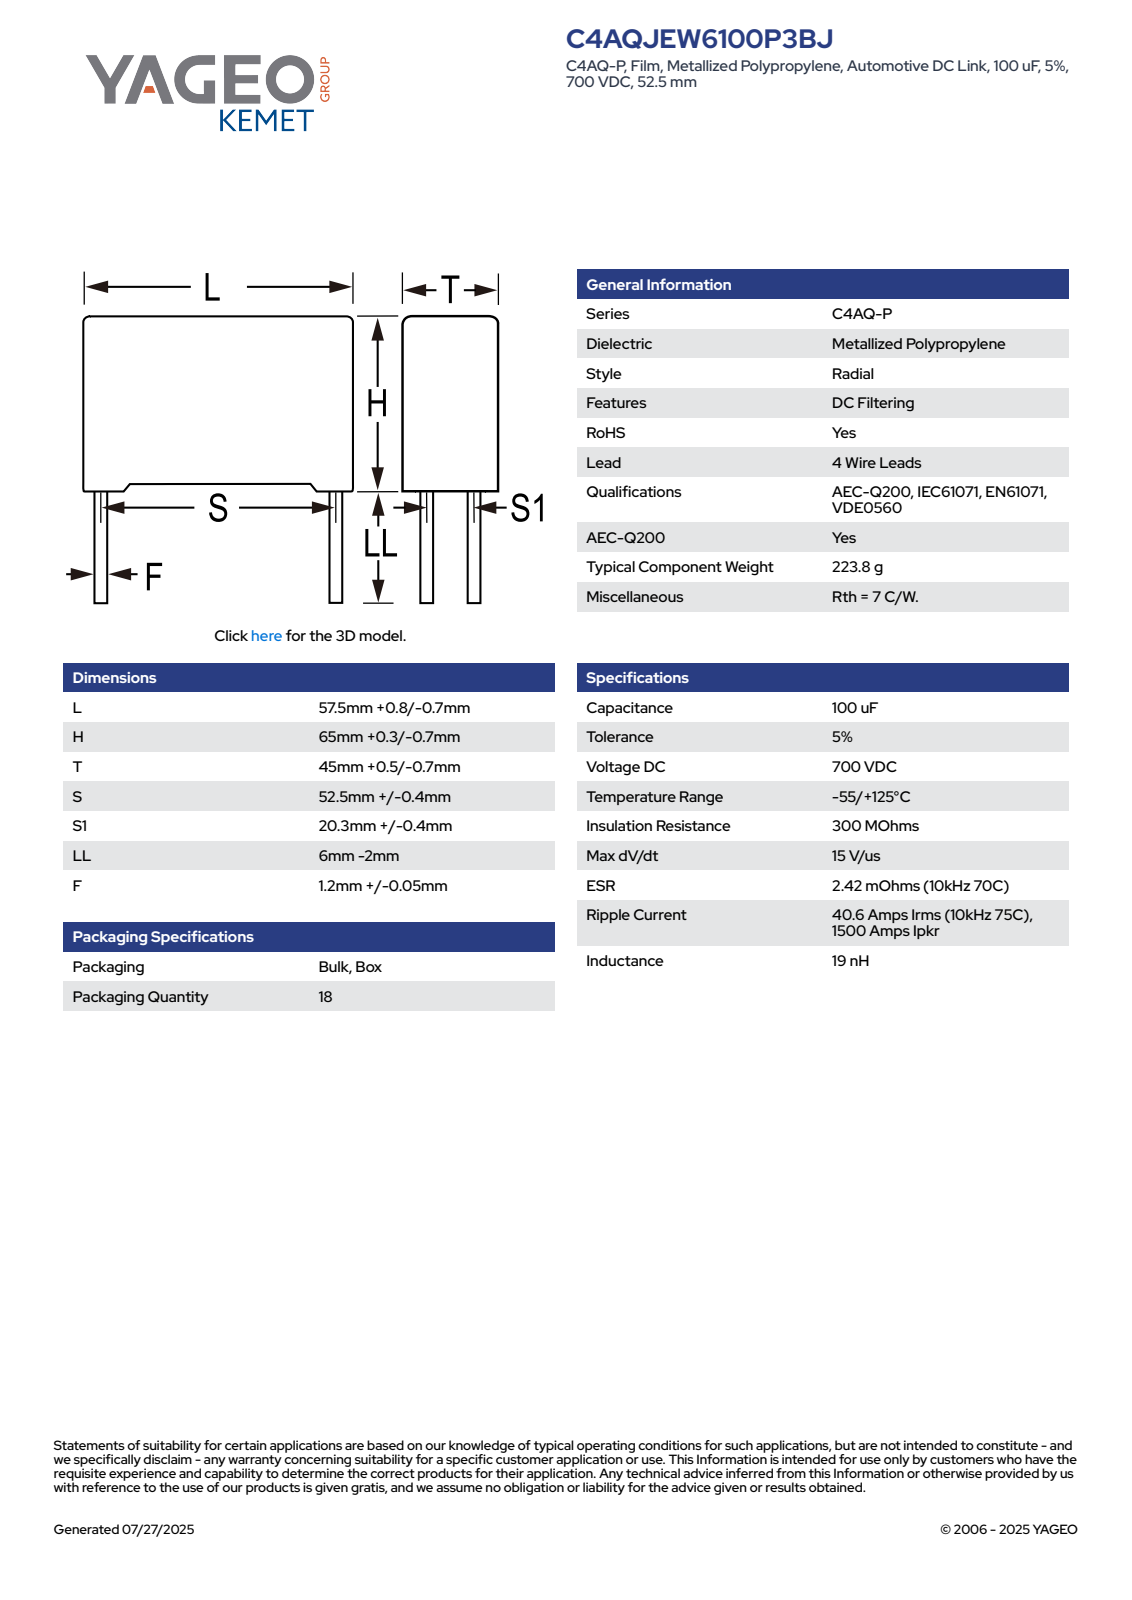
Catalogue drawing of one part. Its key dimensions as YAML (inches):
part_name: "CFP_RB4_57.5X65X45_L58.3H65.3T45.5S52.5S120.3LL4F1.25"
step_written_by: "SolidWorks 2014 (AUTOMOTIVE_DESIGN)"
units: inches
bodies: {solids: 4, faces: 91, planar: 83, cylindrical: 8, other: 0}
overall_size: [2.728, 2.295, 1.792]
volume: 10.3
surface_area: 29.75
round_bosses_or_shafts:
  - {diameter: 0.049, count: 4}
face_to_face_distances: [1.791, 2.295, 2.495, 0.076, 2.571, 0.11, 2.185, 2.075, 1.681, 1.571]
